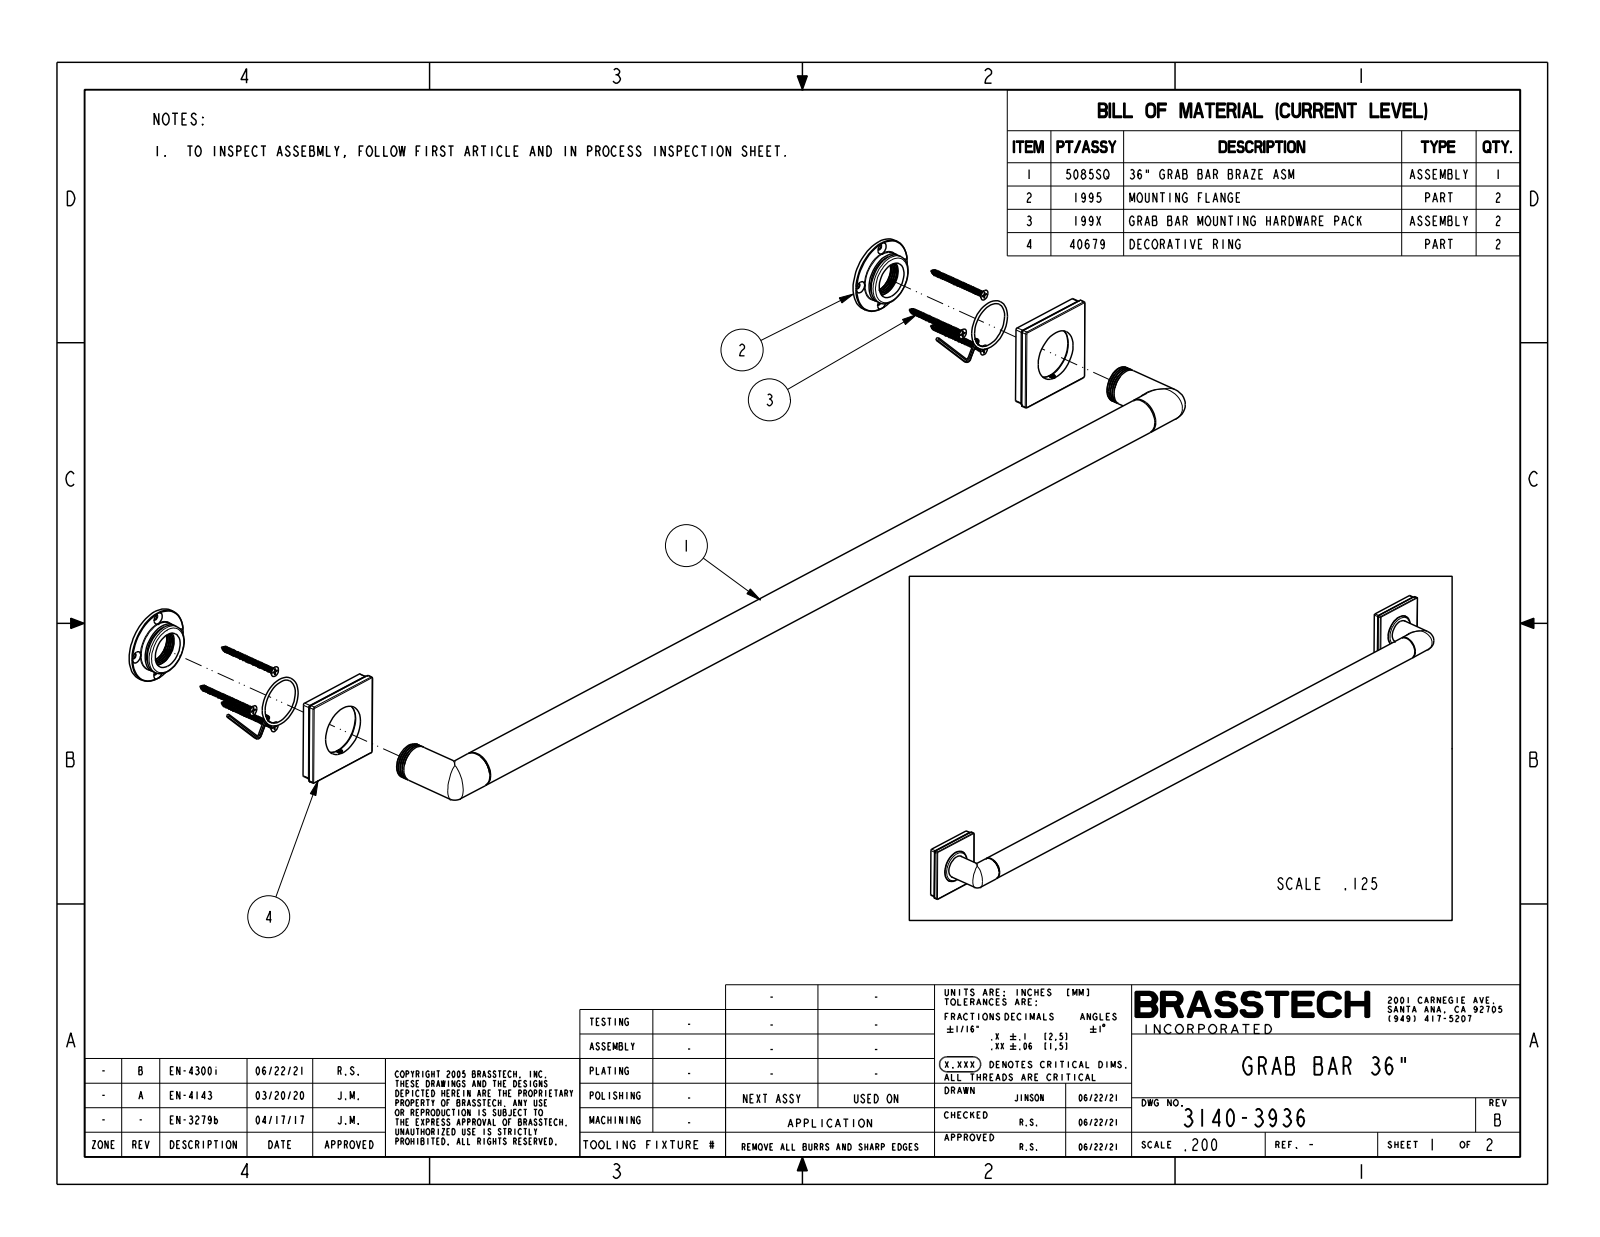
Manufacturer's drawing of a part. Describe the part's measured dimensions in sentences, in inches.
The part is named "3140-3936". Its 3-D file was written by "CREO PARAMETRIC BY PTC INC, 2018400 (CONFIG_CONTROL_DESIGN)". It is 1 solid with 168 faces: 22 planar, 54 cylindrical and 92 other. Overall it measures 39 by 3 by 2.755 inches. Its volume is 57.32 cubic inches and its surface area 198.3 square inches. Round bosses or shafts: 3 of diameter 1.25, 2 of diameter 1.75. Partial cylindrical surfaces (rounded edges, fillets, slot ends): 16 of radius 0.06, 12 of radius 0.03, 6 of radius 0.09. The main face-to-face distances are 0.525, 0.05, 2.95, 2.9, 36, 3, 0.6, 0.075, 36.05, 38.95.
